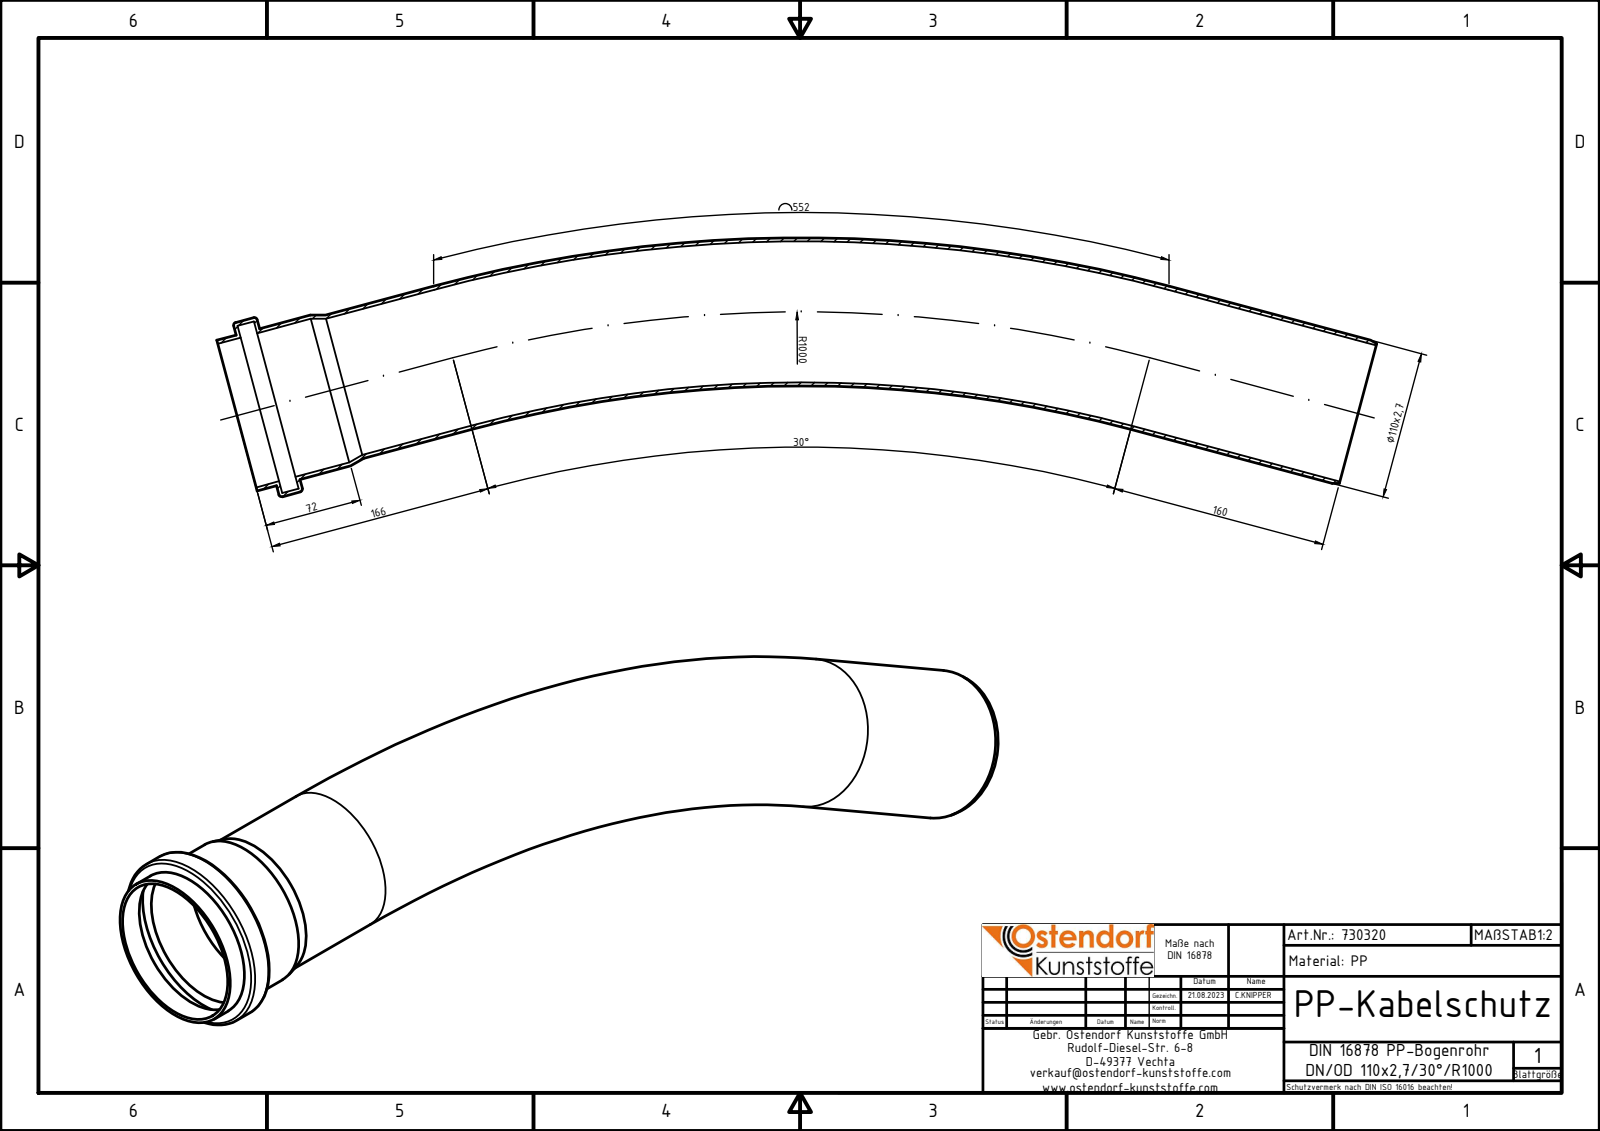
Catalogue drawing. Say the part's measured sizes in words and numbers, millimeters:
The part is named "PP-Bogenrohr_110x27_R1000_30_SM_34874_730320 (003)". Its 3-D file was written by "Autodesk Inventor 2024 (AUTOMOTIVE_DESIGN)". It is 1 solid with 23 faces: 6 planar, 10 cylindrical and 7 other. Overall it measures 831.39 by 327.45 by 134 millimeters. Its volume is 796 781 cubic millimeters and its surface area 592 315 square millimeters. Round holes: 2 of diameter 104.6, 1 of diameter 110.4, 1 of diameter 128.6. Round bosses or shafts: 2 of diameter 110, 1 of diameter 134, 1 of diameter 115.8. The main face-to-face distances are 12.6, 15.31, 2.71, 2.69, 15.29, 18, 15, 17.69, 30.29, 33.
